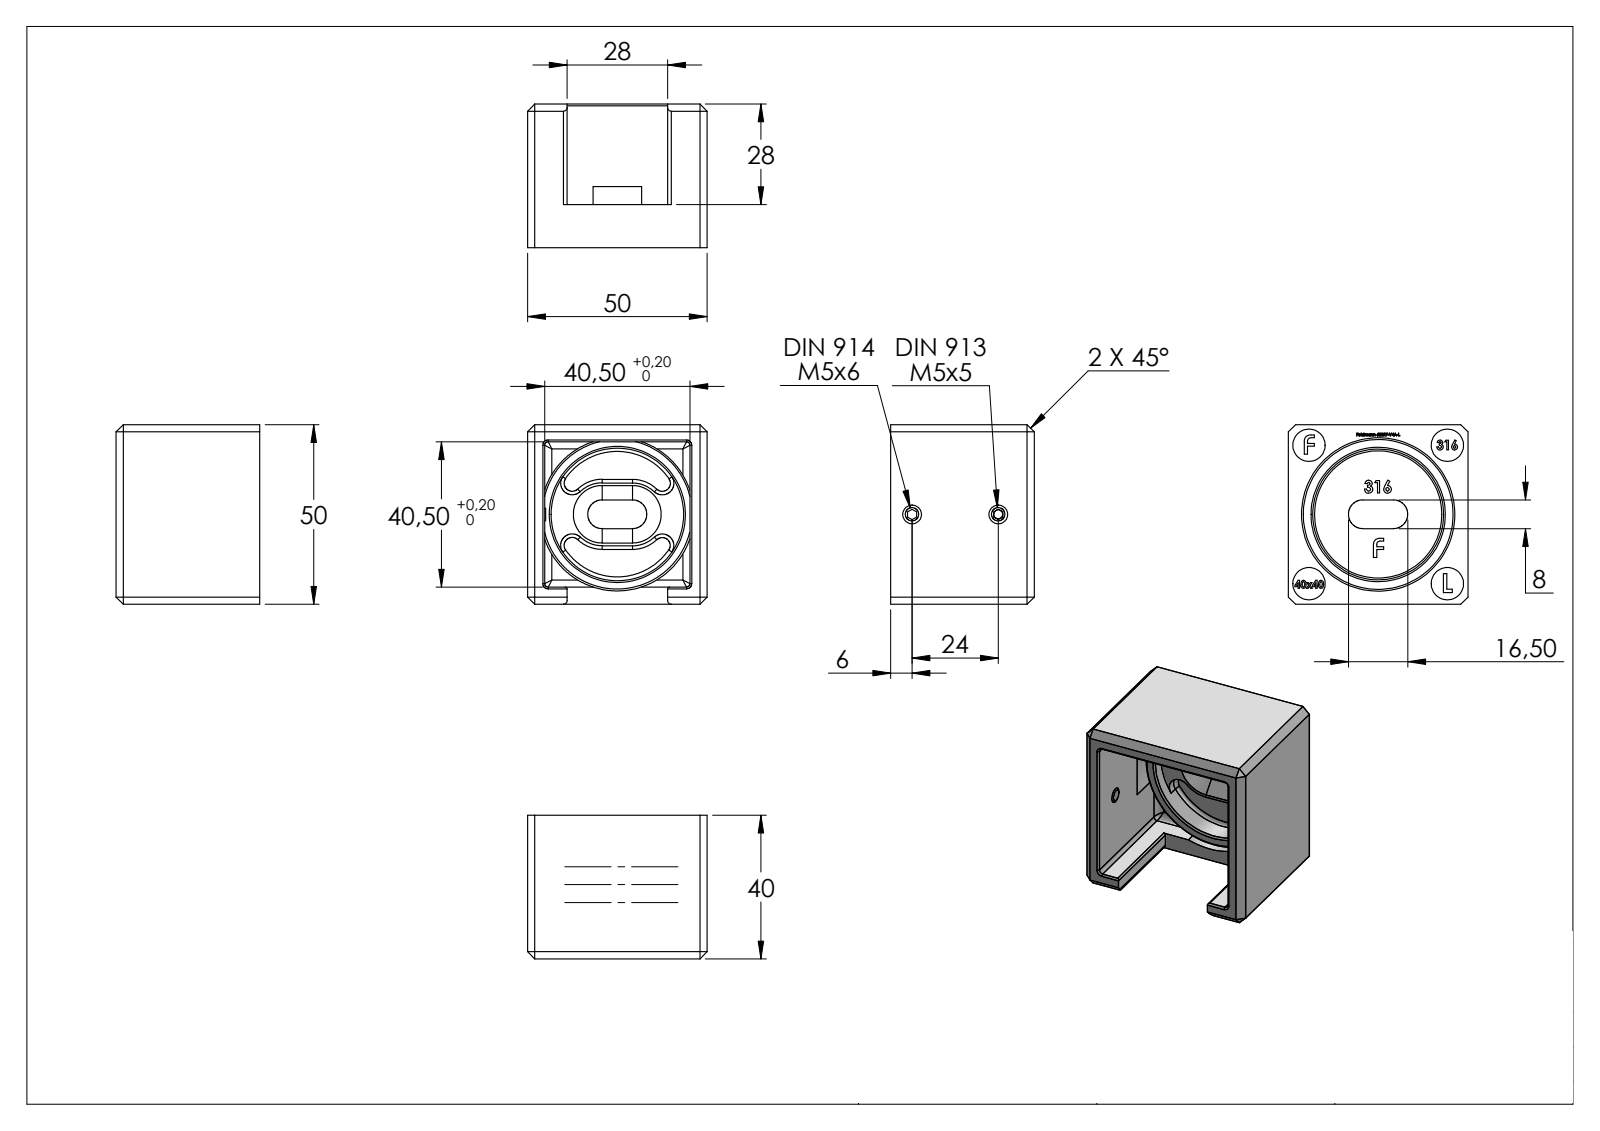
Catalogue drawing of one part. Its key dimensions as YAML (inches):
part_name: "6039X-240-X Teil1_60397-V4A-L Teil1; DIN913_DIN 913 M5x5; DIN914_DIN 914 M5x6; 60397-V4A-L (+1 more)"
step_written_by: "SolidWorks 2015 (CONFIG_CONTROL_DESIGN)"
units: inches
bodies: {solids: 4, faces: 592, planar: 329, cylindrical: 57, other: 206}
overall_size: [1.969, 1.969, 1.575]
volume: 2.23
surface_area: 31.1
round_holes:
  - {diameter: 0.354, count: 4}
  - {diameter: 0.165, count: 2}
  - {diameter: 1.453, count: 1}
round_bosses_or_shafts:
  - {diameter: 0.197, count: 2}
  - {diameter: 1.681, count: 1}
  - {diameter: 1.592, count: 1}
partial_cylinders:
  - {radius: 0.039, count: 8}
  - {radius: 0.079, count: 4}
  - {radius: 0.127, count: 4}
  - {radius: 0.02, count: 2}
  - {radius: 0.157, count: 2}
  - {radius: 0.344, count: 2}
face_to_face_distances: [0.187, 1.781, 1.969, 1.594, 0.039, 1.535, 0.02, 0.11, 0.071, 1.575]
hole_center_spacings: [1.073, 1.517, 2.146, 0.945]
